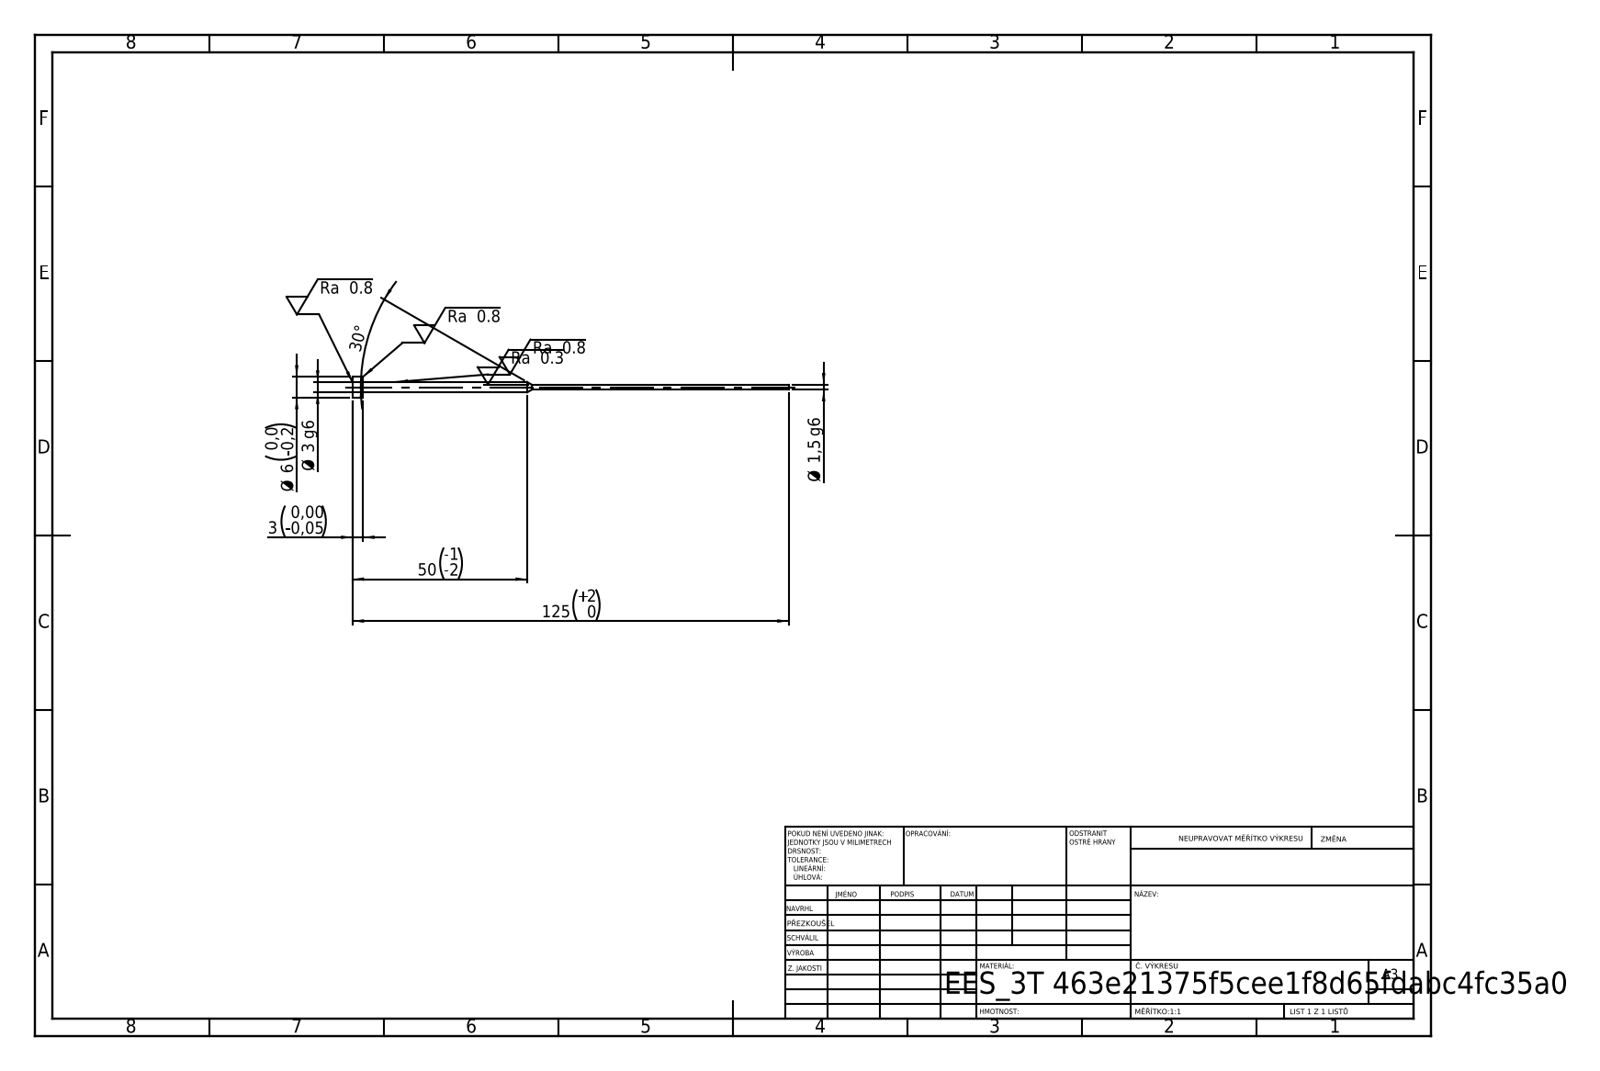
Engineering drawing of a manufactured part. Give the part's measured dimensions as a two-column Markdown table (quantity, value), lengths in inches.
| quantity | value |
| --- | --- |
| STEP written by | SolidWorks 2019 (CONFIG_CONTROL_DESIGN) |
| units | inches |
| bodies | 1 solid, 11 faces (3 planar, 6 cylindrical, 2 other) |
| overall size | 4.921 × 0.236 × 0.236 |
| volume | 0.034 in³ |
| surface area | 1.41 in² |
| round bosses / shafts (diameter × count) | 0.236 × 1, 0.118 × 1, 0.059 × 1 |
| main face-to-face distances | 0.118, 4.803, 4.921 |
